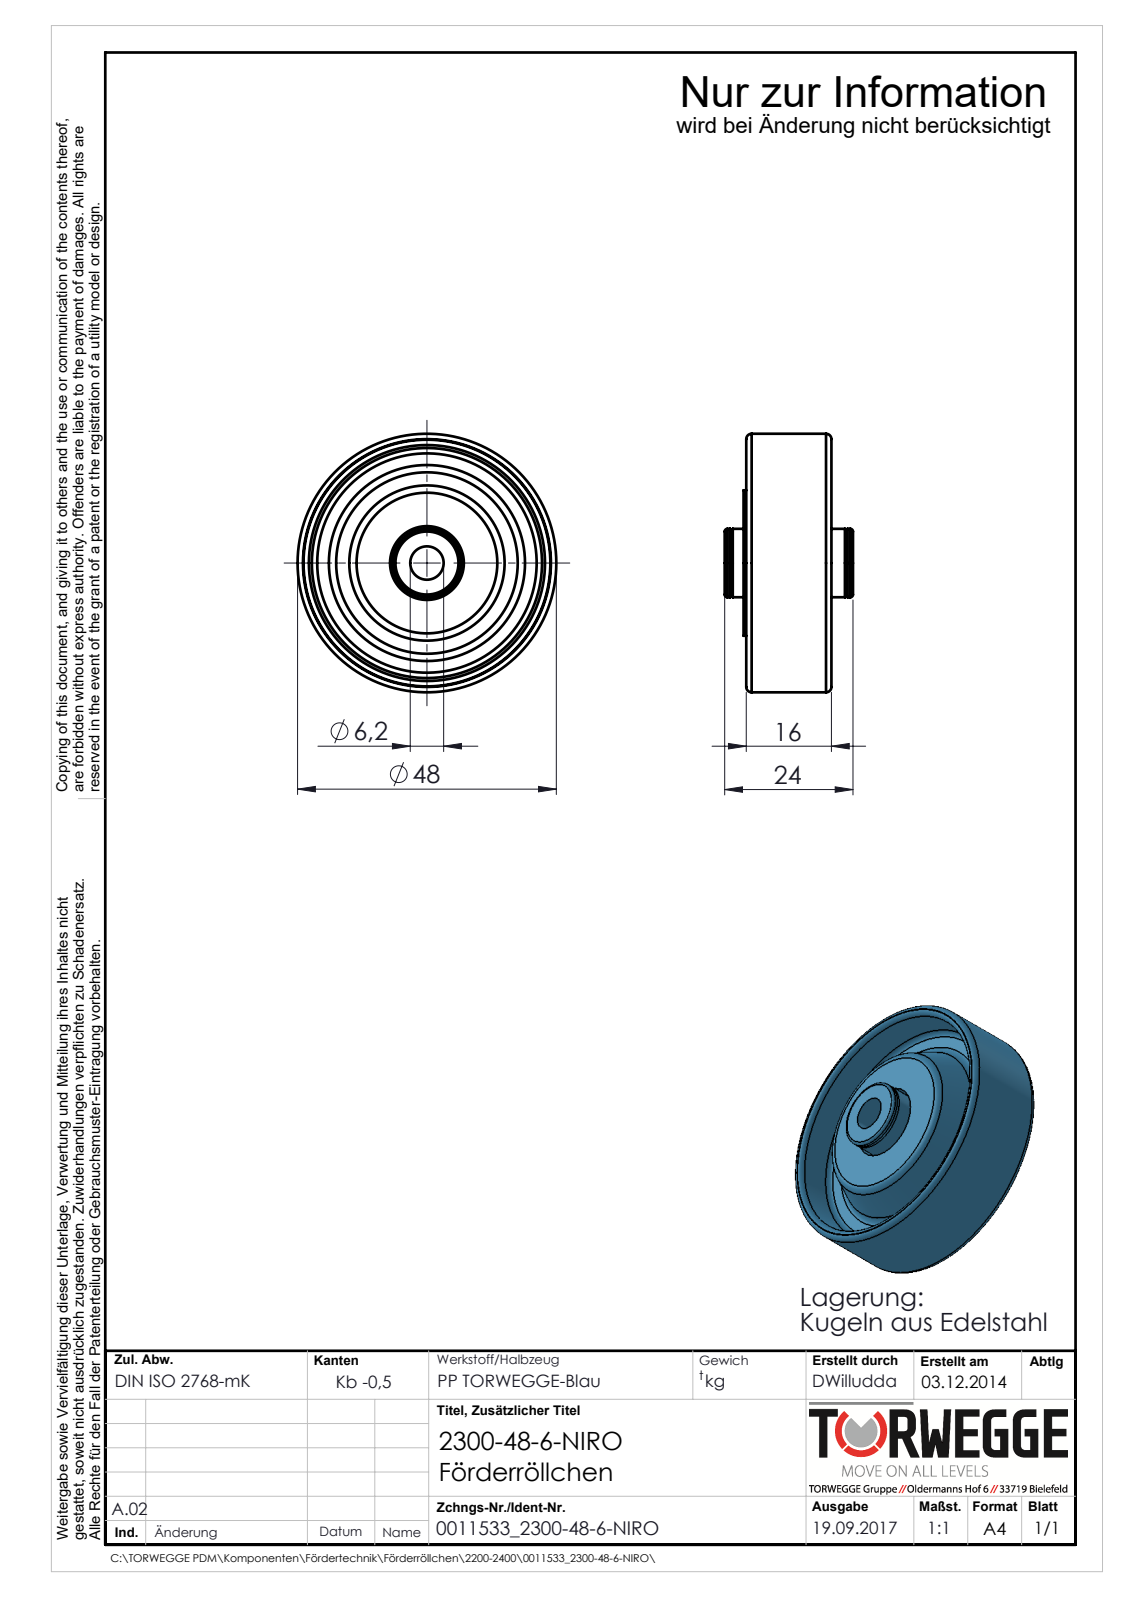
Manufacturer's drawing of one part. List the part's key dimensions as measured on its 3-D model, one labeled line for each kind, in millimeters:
Part name (STEP PRODUCT): 0011533_2300-48-6-NIRO
STEP written by: SolidWorks 2016 (AUTOMOTIVE_DESIGN)
Units: millimetres
Bodies: 1 solid, 69 faces (11 planar, 18 cylindrical, 40 other)
Overall size (bounding box): 48 × 48 × 23.8
Volume: 19 452 mm³ · Surface area: 9 463 mm²
Round holes (diameter × count): ⌀6.2 ×1, ⌀13.7 ×1
Round bosses / shafts (diameter × count): ⌀48 ×1, ⌀27 ×1, ⌀12.7 ×1
Main face-to-face distances: 16.3, 9.05, 6.75, 7.25, 2.3, 9.55, 10.75, 13.05, 4, 3.5
